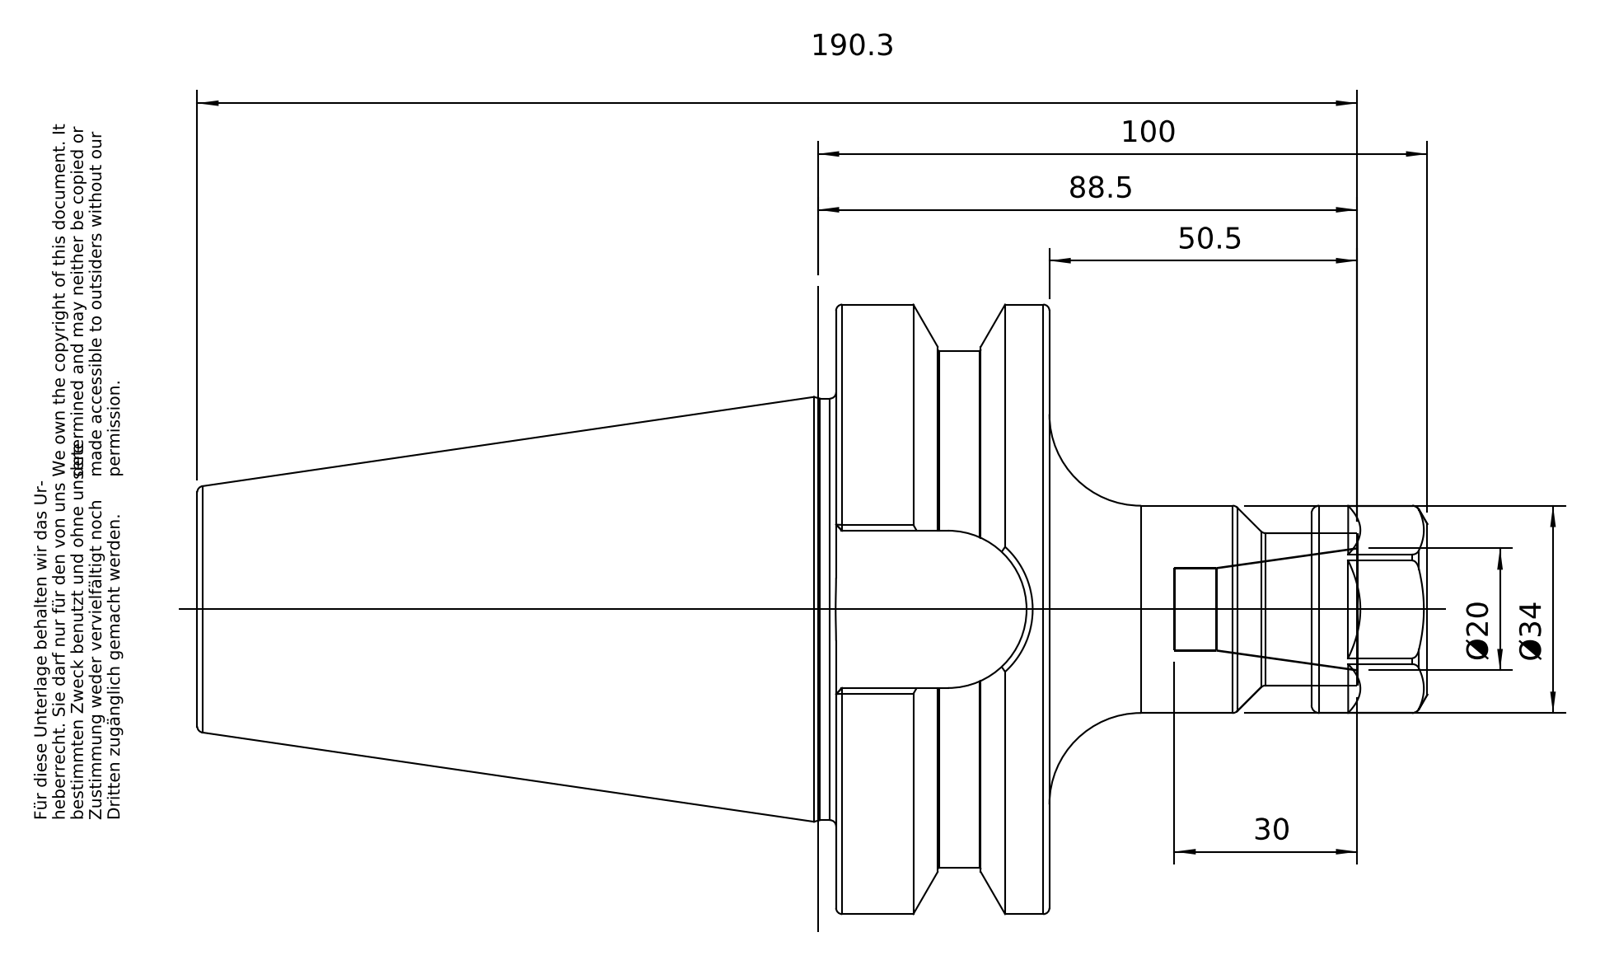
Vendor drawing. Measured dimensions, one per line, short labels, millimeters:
name: 50-521-20; 83-912-20; 50-521-20_ASM
written by: PRO/ENGINEER BY PARAMETRIC TECHNOLOGY CORPORATION, 2010430 (CONFIG_CONTROL_DESIGN)
unit: mm
bodies: 2 solids, 128 faces (34 planar, 26 cylindrical, 68 other)
size: 201.8 × 99.97 × 99.97
volume: 522 014 mm³; area: 60 831 mm²
holes: 1× ⌀13.5, 1× ⌀20.75, 1× ⌀25.02, 1× ⌀25.7
bosses: 1× ⌀99.97, 1× ⌀84.75, 1× ⌀69.15, 1× ⌀34, 1× ⌀25, 1× ⌀24.01
rounds: 1× R12.9
face distances: 35, 78, 43, 70.4, 30, 97, 62, 19, 104.8, 139.8
